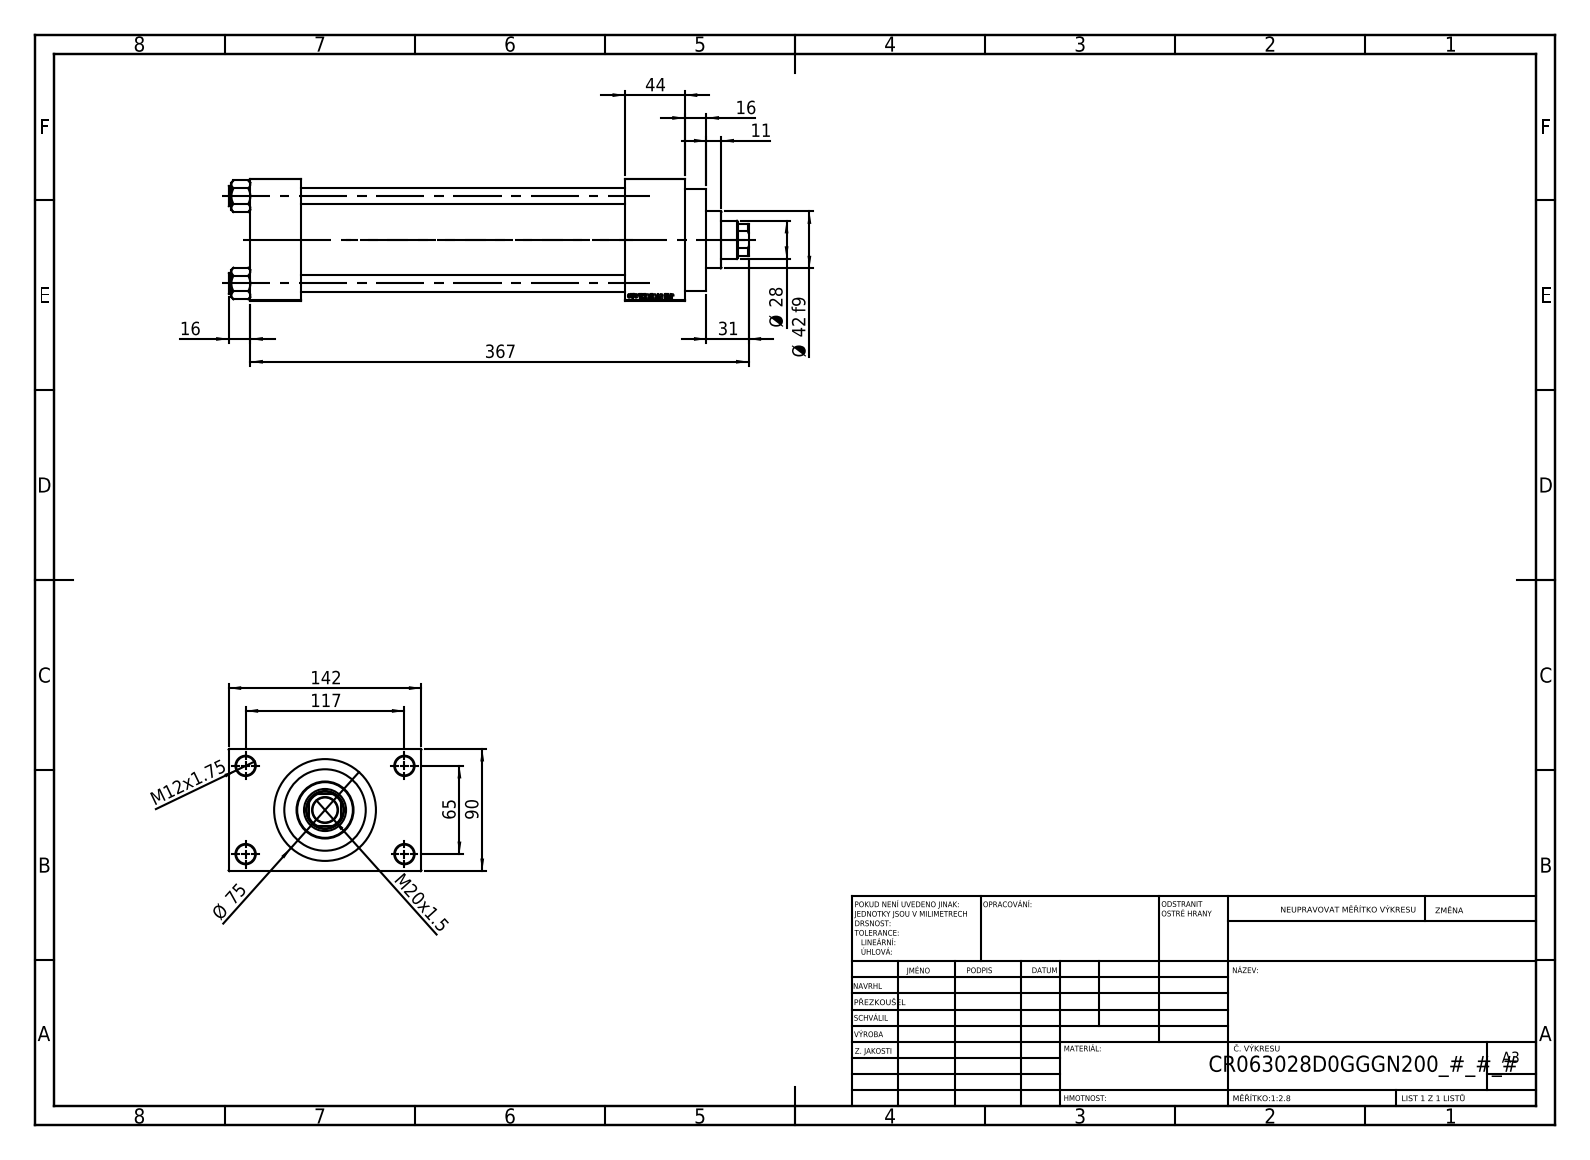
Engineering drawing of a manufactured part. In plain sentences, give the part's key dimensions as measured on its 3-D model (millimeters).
The part is named "V215CR_D_TYCINKA; V215_VC_A; NUT_M5_D; V215CR_D_Body (+1 more)". Its 3-D file was written by "SolidWorks 2019 (CONFIG_CONTROL_DESIGN)". It is 11 solids with 1104 faces: 497 planar, 89 cylindrical and 518 other. Overall it measures 383 by 142 by 90 millimeters. Its volume is 1 409 000 cubic millimeters and its surface area 316 228 square millimeters. Round holes: 4 of diameter 12, 4 of diameter 14, 2 of diameter 7, 2 of diameter 20.96, 2 of diameter 30, 1 of diameter 18.5, 1 of diameter 28, 1 of diameter 31, 1 of diameter 50, 1 of diameter 60, 1 of diameter 63. Round bosses or shafts: 4 of diameter 15, 1 of diameter 75, 1 of diameter 69, 1 of diameter 42. Partial cylindrical surfaces (rounded edges, fillets, slot ends): 1 of radius 13.5. The main face-to-face distances are 90, 239, 37, 276, 283, 320, 44, 26, 116, 142. The hole center spacings are 26.35, 45.47, 64.3, 66.92, 69.81, 90.65, 111.34, 65.
